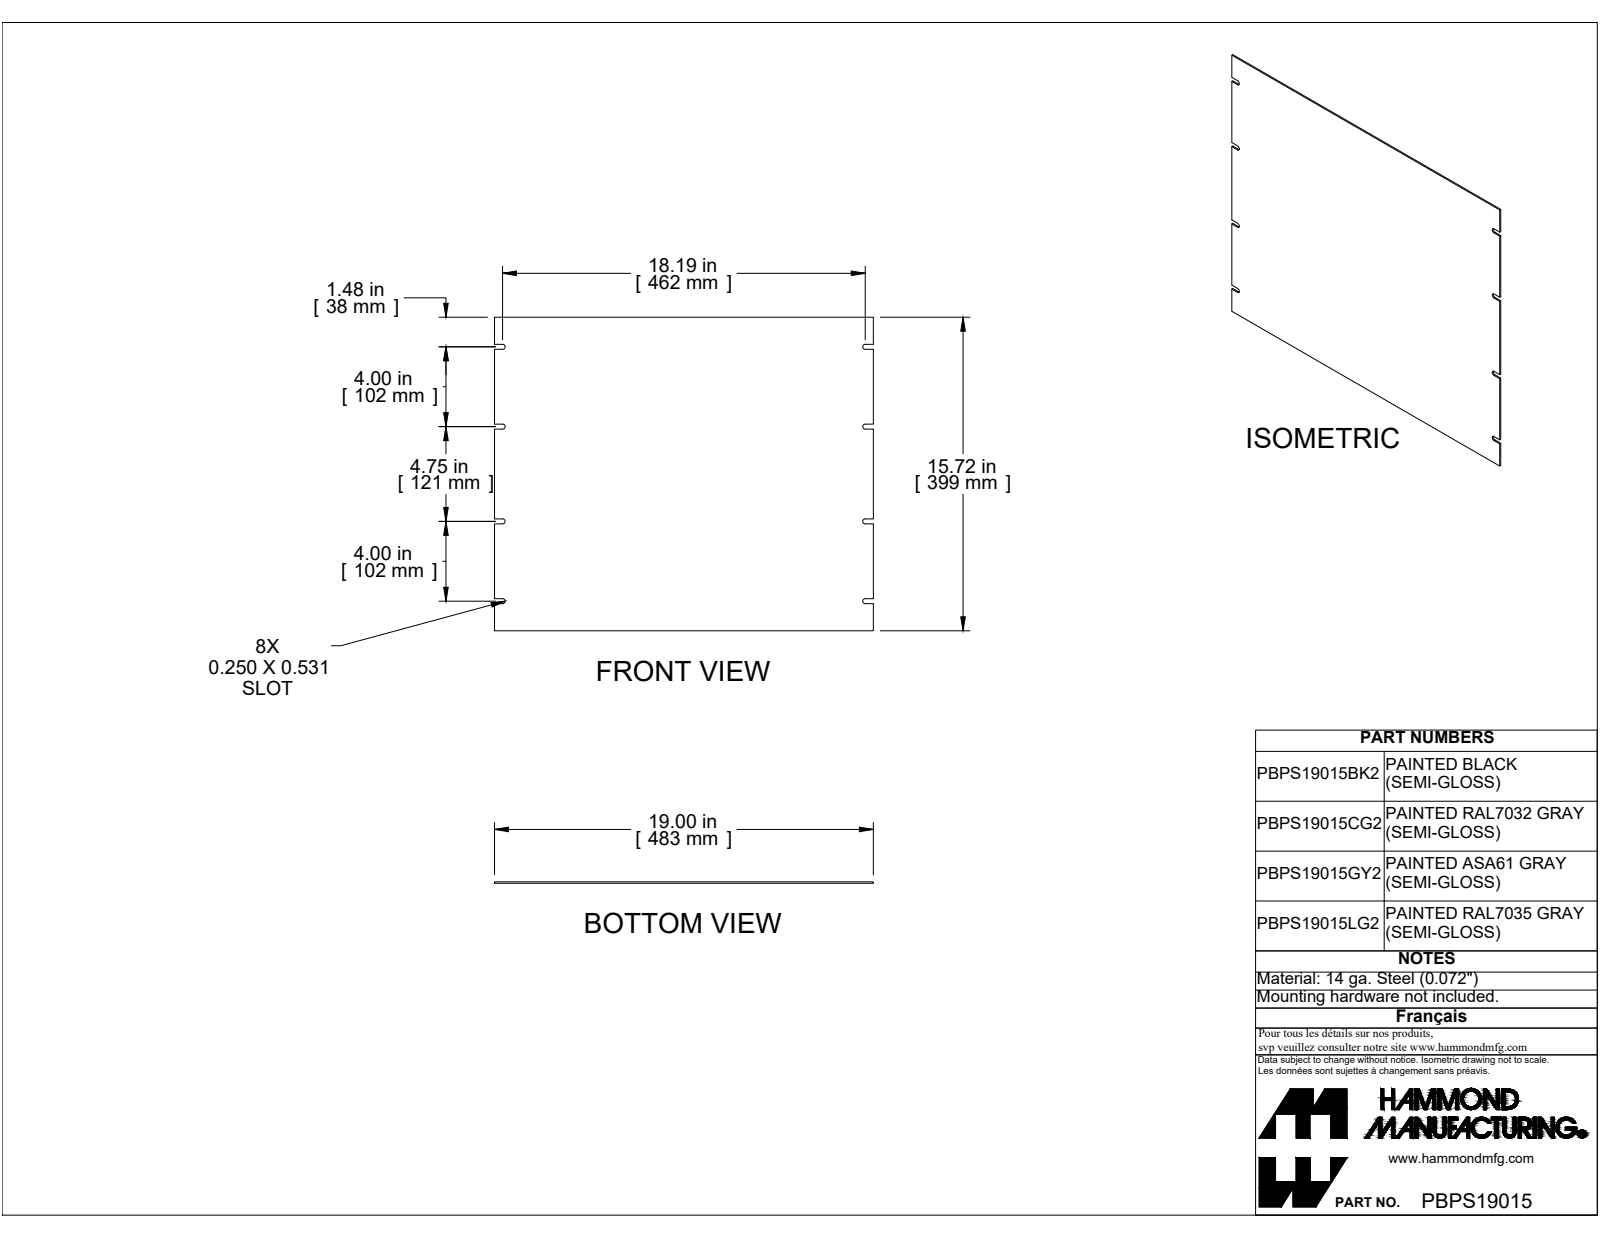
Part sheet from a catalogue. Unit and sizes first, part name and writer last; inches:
Units: inches
Overall size (bounding box): 19 × 15.718 × 0.072
Partial cylindrical surfaces — rounded edges, fillets, slot ends (radius × count): R0.125 ×8
Main face-to-face distances: 0.072, 15.718, 19, 0.25, 4, 8.75, 5.359, 10.359, 5.609, 10.109
Volume: 21.43 in³ · Surface area: 600.8 in²
Bodies: 1 solid, 38 faces (30 planar, 8 cylindrical, 0 other)
Part name (STEP PRODUCT): PBPS19015LG2
STEP written by: SolidWorks 2019 (CONFIG_CONTROL_DESIGN)
